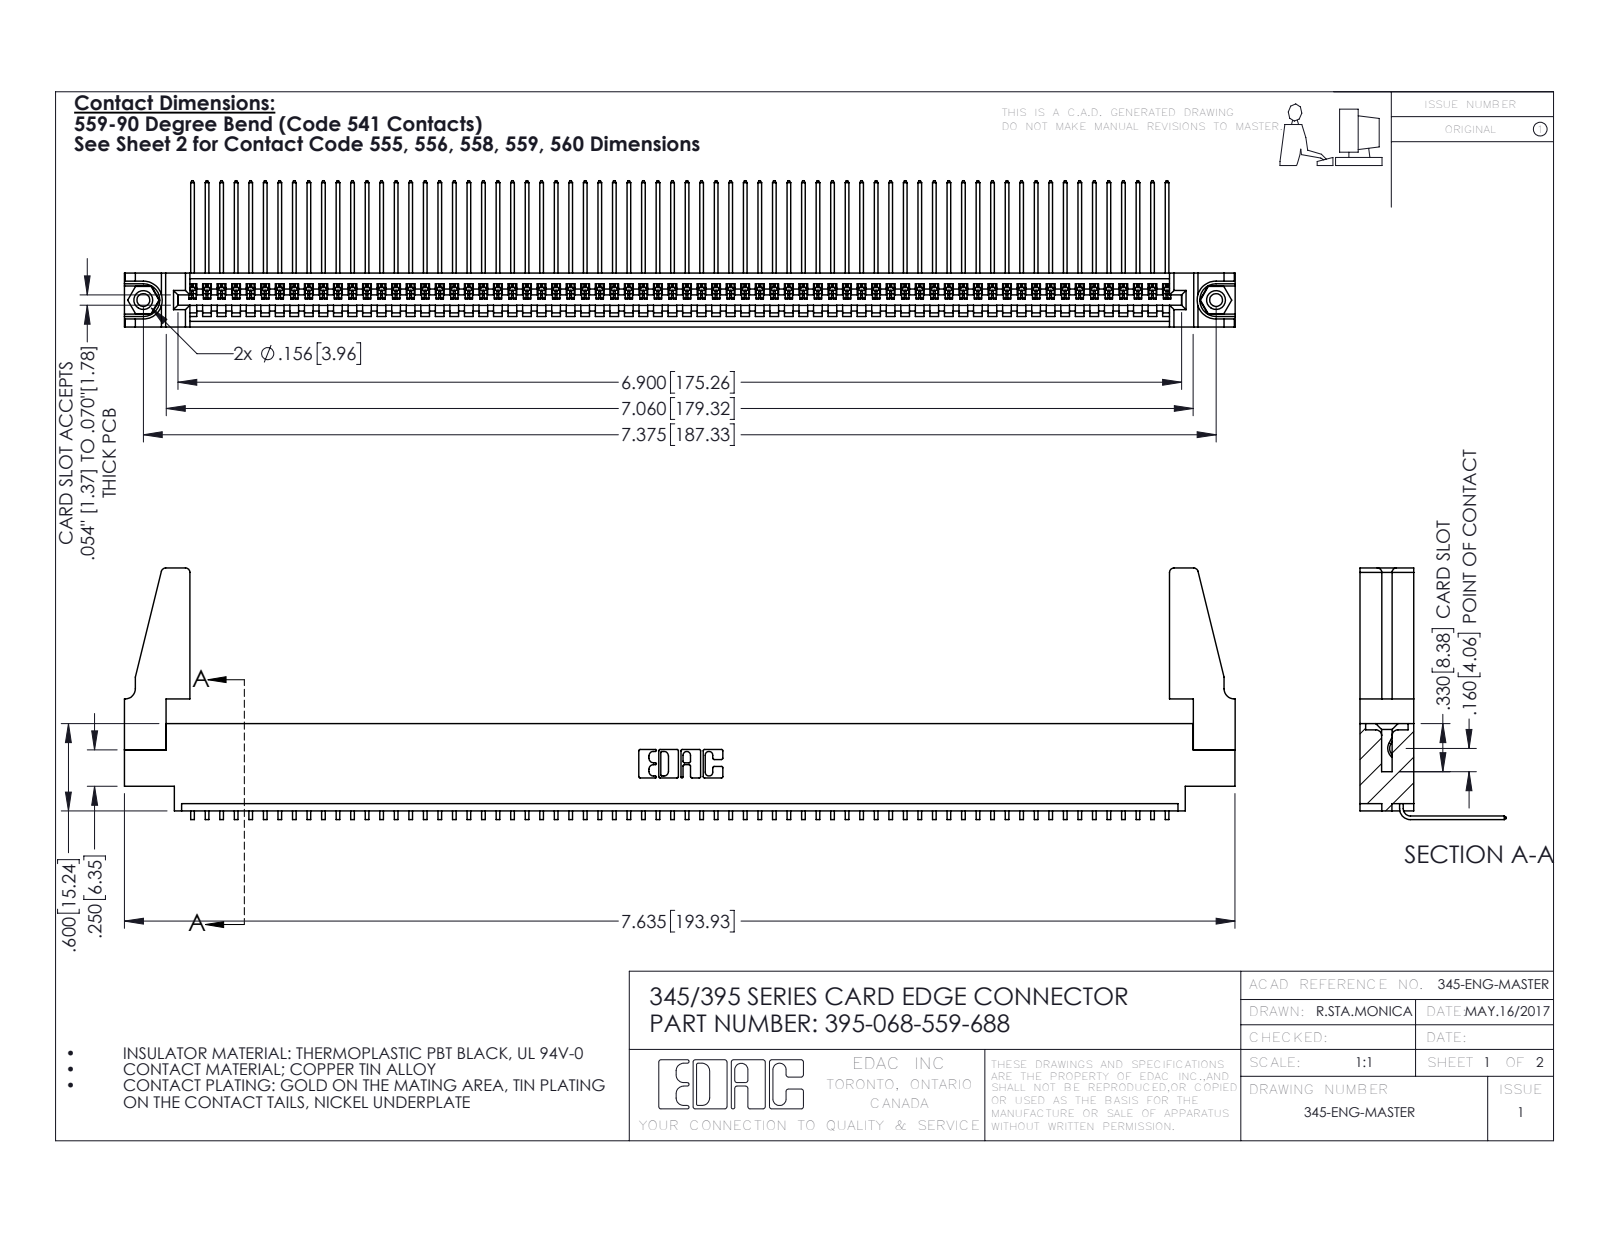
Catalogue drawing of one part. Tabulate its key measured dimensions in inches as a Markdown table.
| quantity | value |
| --- | --- |
| part name | 345 Part_0.170 Offset - 0.156 Dia-TH; 345-220-078_345-220-088; 345-250-001_345-250-001-102; 395-068-559-688 (+1 more) |
| STEP written by | SolidWorks 2016 (CONFIG_CONTROL_DESIGN) |
| units | inches |
| bodies | 73 solids, 4334 faces (3012 planar, 1306 cylindrical, 16 other) |
| overall size | 7.636 × 1.729 × 1.005 |
| volume | 1.343 in³ |
| surface area | 46.28 in² |
| round holes (diameter × count) | 0.089 × 2, 0.125 × 2, 0.156 × 2, 0.064 × 1 |
| round bosses / shafts (diameter × count) | 0.155 × 2 |
| partial cylindrical surfaces (radius × count) | 0.006 × 136, 0.01 × 22, 0.03 × 8, 0.007 × 6, 0.031 × 6, 0.026 × 3, 0.031 × 2, 0.04 × 2 |
| main face-to-face distances | 0.072, 0.298, 0.37, 0.098, 0.272, 0.025, 0.2, 0.225, 0.175, 0.149 |
| hole center spacings | 0.27, 7.139, 7.375 |
